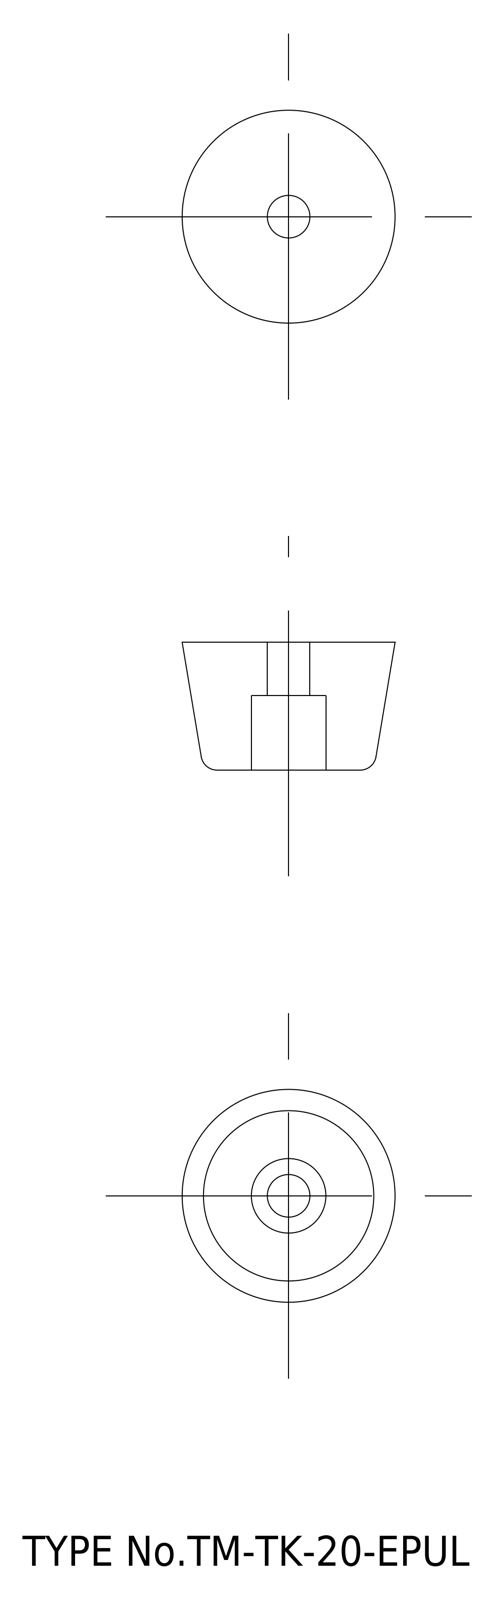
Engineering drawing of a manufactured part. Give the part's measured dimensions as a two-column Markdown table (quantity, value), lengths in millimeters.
| quantity | value |
| --- | --- |
| part name | washer; rubber foot |
| STEP written by | spGate 15.6.1 (AUTOMOTIVE_DESIGN) |
| units | millimeters |
| bodies | 2 solids, 20 faces (6 planar, 10 cylindrical, 4 other) |
| overall size | 20 × 20 × 12 |
| volume | 2 724 mm³ |
| surface area | 1 636 mm² |
| round holes (diameter × count) | 4 × 1, 7 × 1, 10 × 1 |
| main face-to-face distances | 4.2, 0.8, 5, 7, 7.8, 12 |
